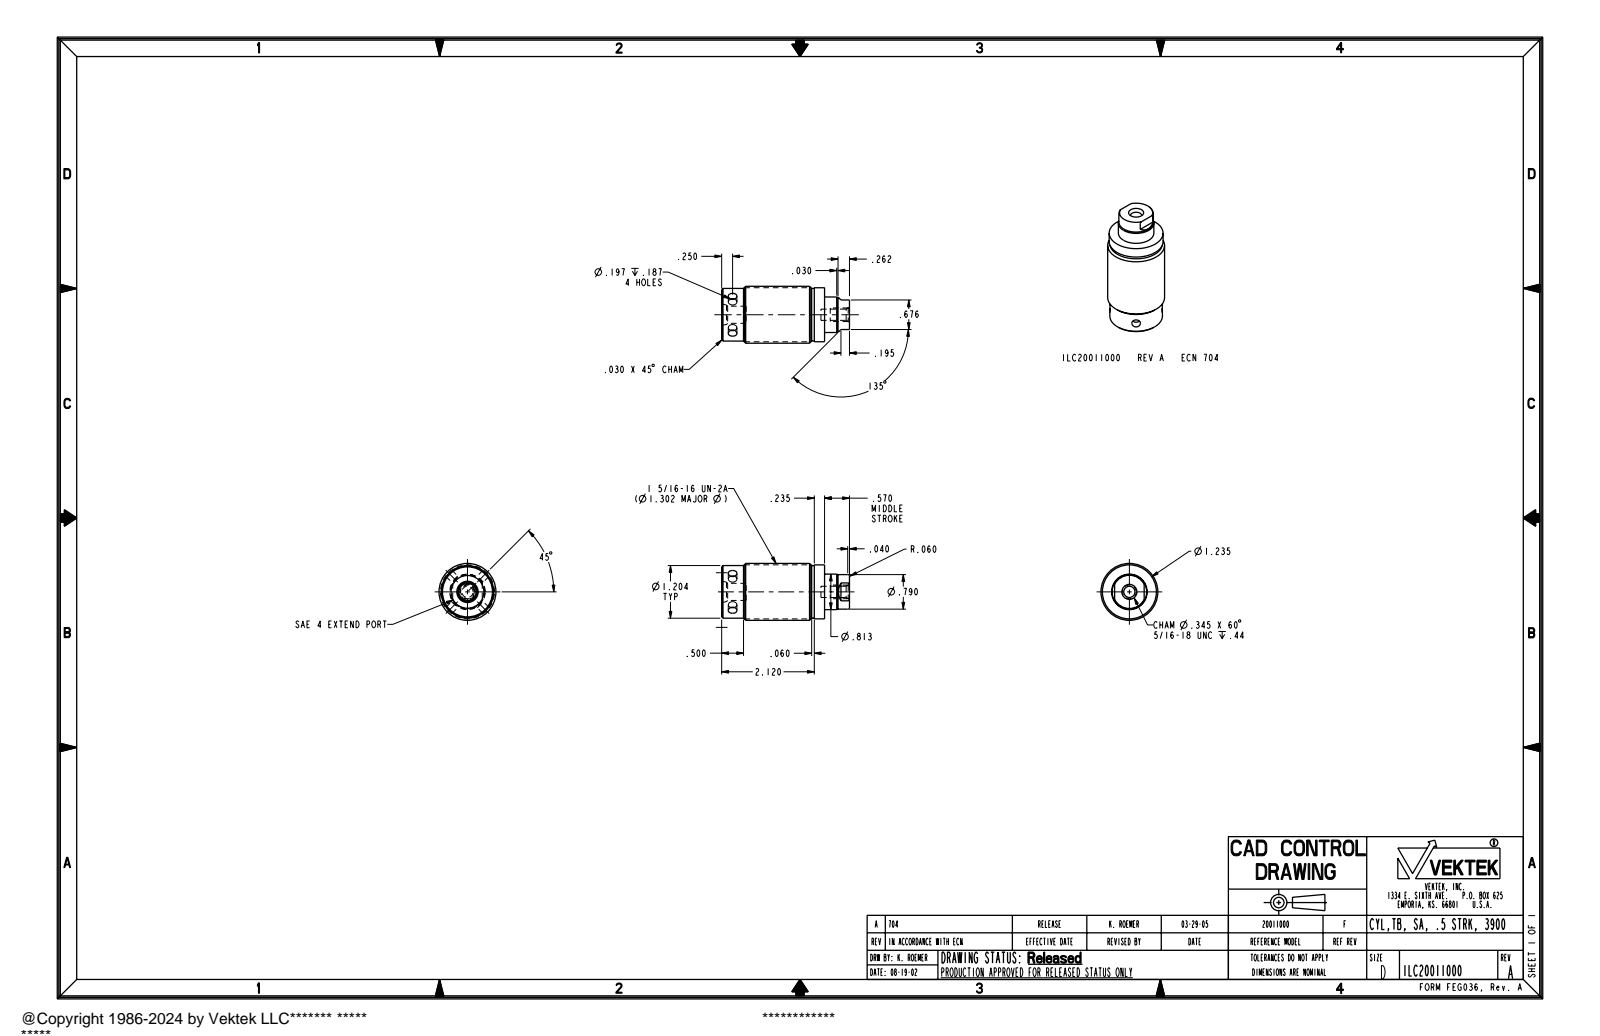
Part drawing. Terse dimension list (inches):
name: ILC20011000
written by: PRO/ENGINEER BY PARAMETRIC TECHNOLOGY CORPORATION, 2004290 (AUTOMOTIVE_DESIGN_CC2)
unit: in
bodies: 1 solid, 62 faces (16 planar, 30 cylindrical, 16 other)
size: 2.925 × 1.302 × 1.302
volume: 3.131 in³; area: 21.25 in²
holes: 2× ⌀0.197, 1× ⌀0.257, 1× ⌀0.392, 1× ⌀0.75
bosses: 1× ⌀1.302, 1× ⌀1.237, 1× ⌀1.235, 1× ⌀1.204, 1× ⌀0.813, 1× ⌀0.79, 1× ⌀0.312
face distances: 2.355, 0.57, 2.925, 2.915, 2.345, 2.365, 1.795, 0.55, 0.56, 0.676
